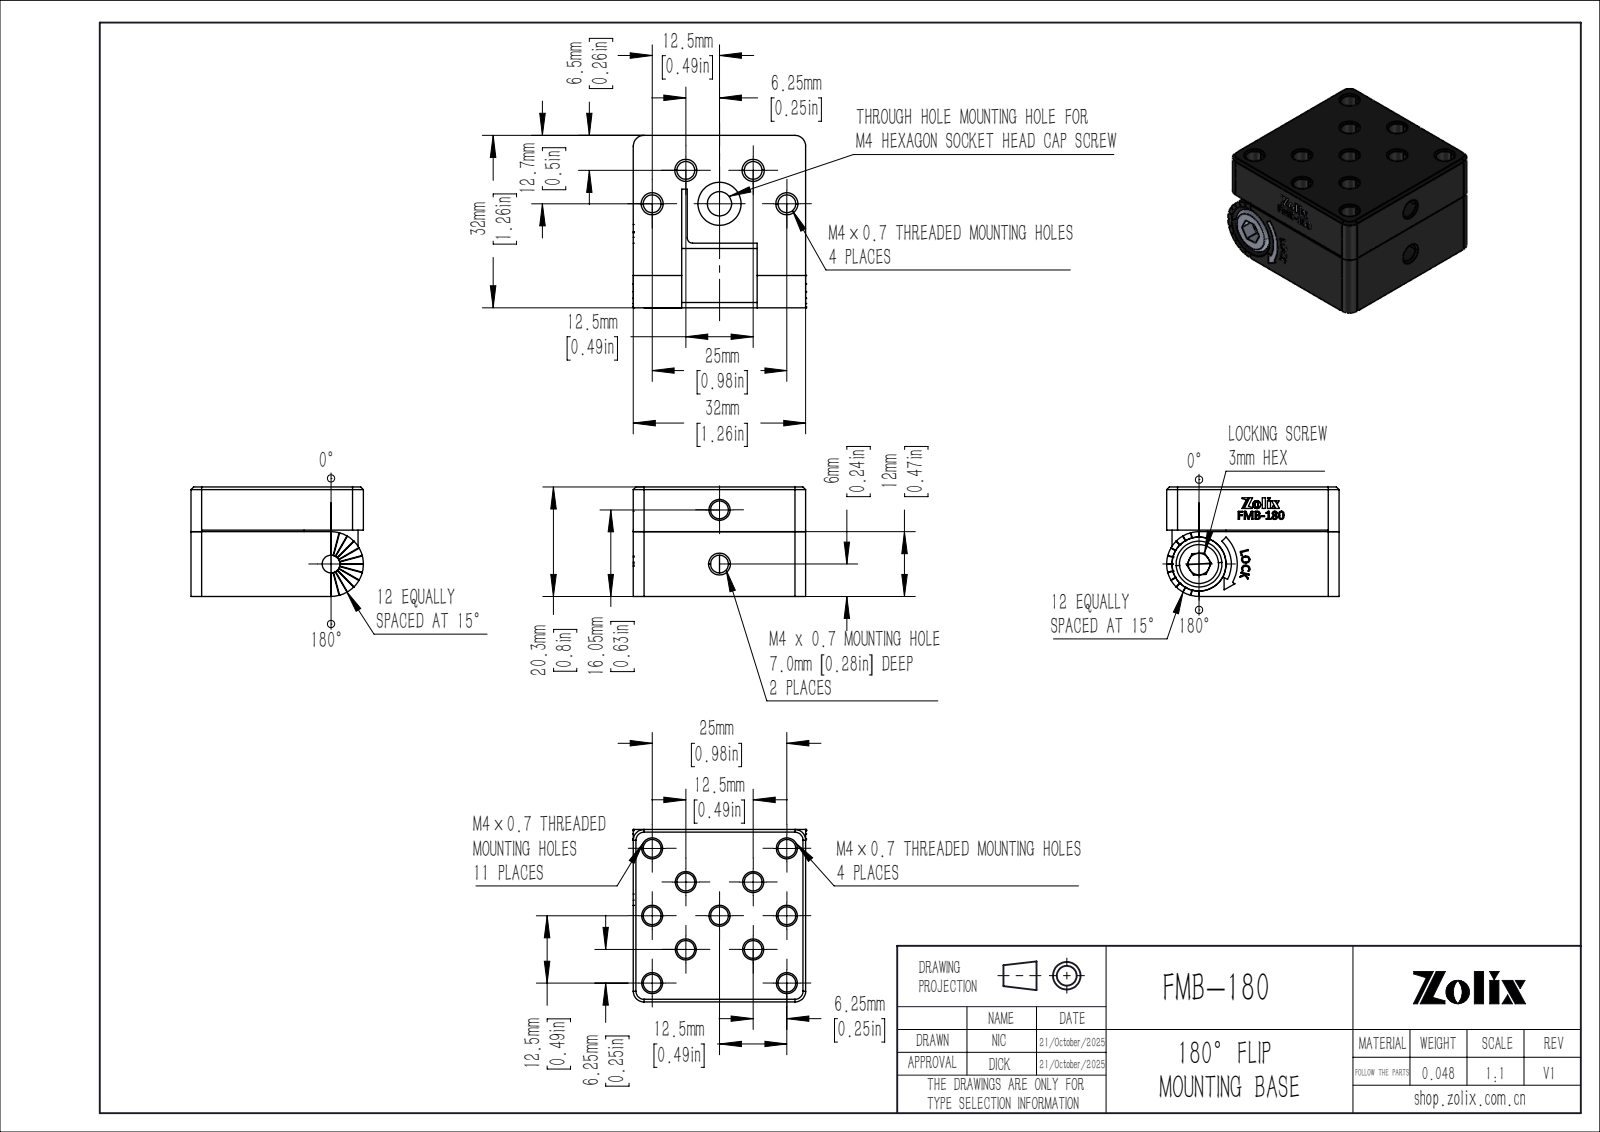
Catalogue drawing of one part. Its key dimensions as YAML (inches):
part_name: "FMB-180"
step_written_by: "SolidWorks 2020 (CONFIG_CONTROL_DESIGN)"
units: inches
bodies: {solids: 3, faces: 620, planar: 394, cylindrical: 62, other: 164}
overall_size: [1.26, 1.26, 0.799]
volume: 1.087
surface_area: 15.13
round_holes:
  - {diameter: 0.13, count: 18}
  - {diameter: 0.177, count: 1}
  - {diameter: 0.197, count: 1}
  - {diameter: 0.315, count: 1}
  - {diameter: 0.394, count: 1}
round_bosses_or_shafts:
  - {diameter: 0.335, count: 1}
partial_cylinders:
  - {radius: 0.079, count: 4}
  - {radius: 0.039, count: 1}
  - {radius: 0.197, count: 1}
  - {radius: 0.236, count: 1}
face_to_face_distances: [0.315, 0.472, 0.327, 1.26, 0.799, 0.484, 0.354, 0.906, 0.039, 0.394]
hole_center_spacings: [0.492, 0.348, 0.778, 0.696, 0.984, 0.272, 0.346, 0.448]
